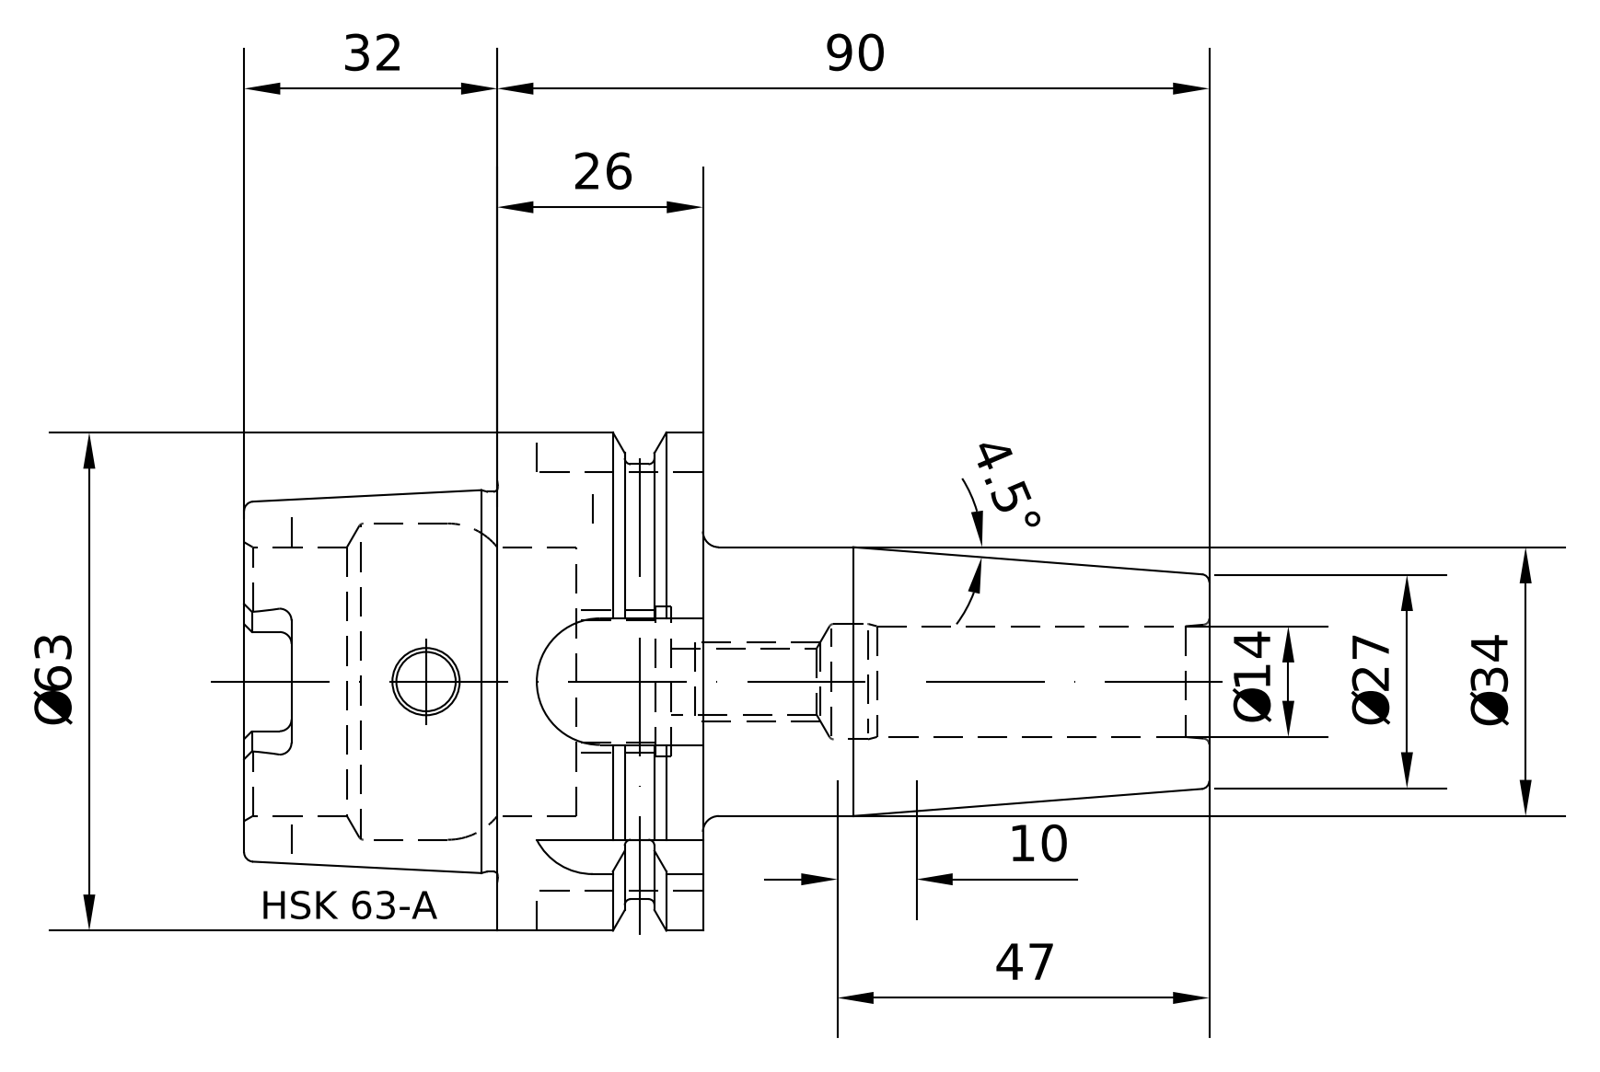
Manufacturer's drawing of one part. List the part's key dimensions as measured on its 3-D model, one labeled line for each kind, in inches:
Part name (STEP PRODUCT): A63-140-14
STEP written by: PRO/ENGINEER BY PARAMETRIC TECHNOLOGY CORPORATION, 2010430 (CONFIG_CONTROL_DESIGN)
Units: inches
Bodies: 1 solid, 173 faces (57 planar, 48 cylindrical, 68 other)
Overall size (bounding box): 4.803 × 2.48 × 2.48
Volume: 7.623 in³ · Surface area: 47.34 in²
Round holes (diameter × count): ⌀0.295 ×1, ⌀0.394 ×1, ⌀0.551 ×1, ⌀0.666 ×1, ⌀0.721 ×1, ⌀0.735 ×1, ⌀1.339 ×1, ⌀1.575 ×1
Round bosses / shafts (diameter × count): ⌀2.48 ×1, ⌀2.165 ×1, ⌀1.891 ×1, ⌀0.709 ×1
Partial cylindrical surfaces — rounded edges, fillets, slot ends (radius × count): R0.059 ×6, R0.118 ×4, R0.315 ×1, R0.316 ×1, R0.355 ×1
Main face-to-face distances: 1.024, 0.394, 0.63, 1.26, 1.654, 2.283, 4.803, 3.543, 3.15, 2.52
